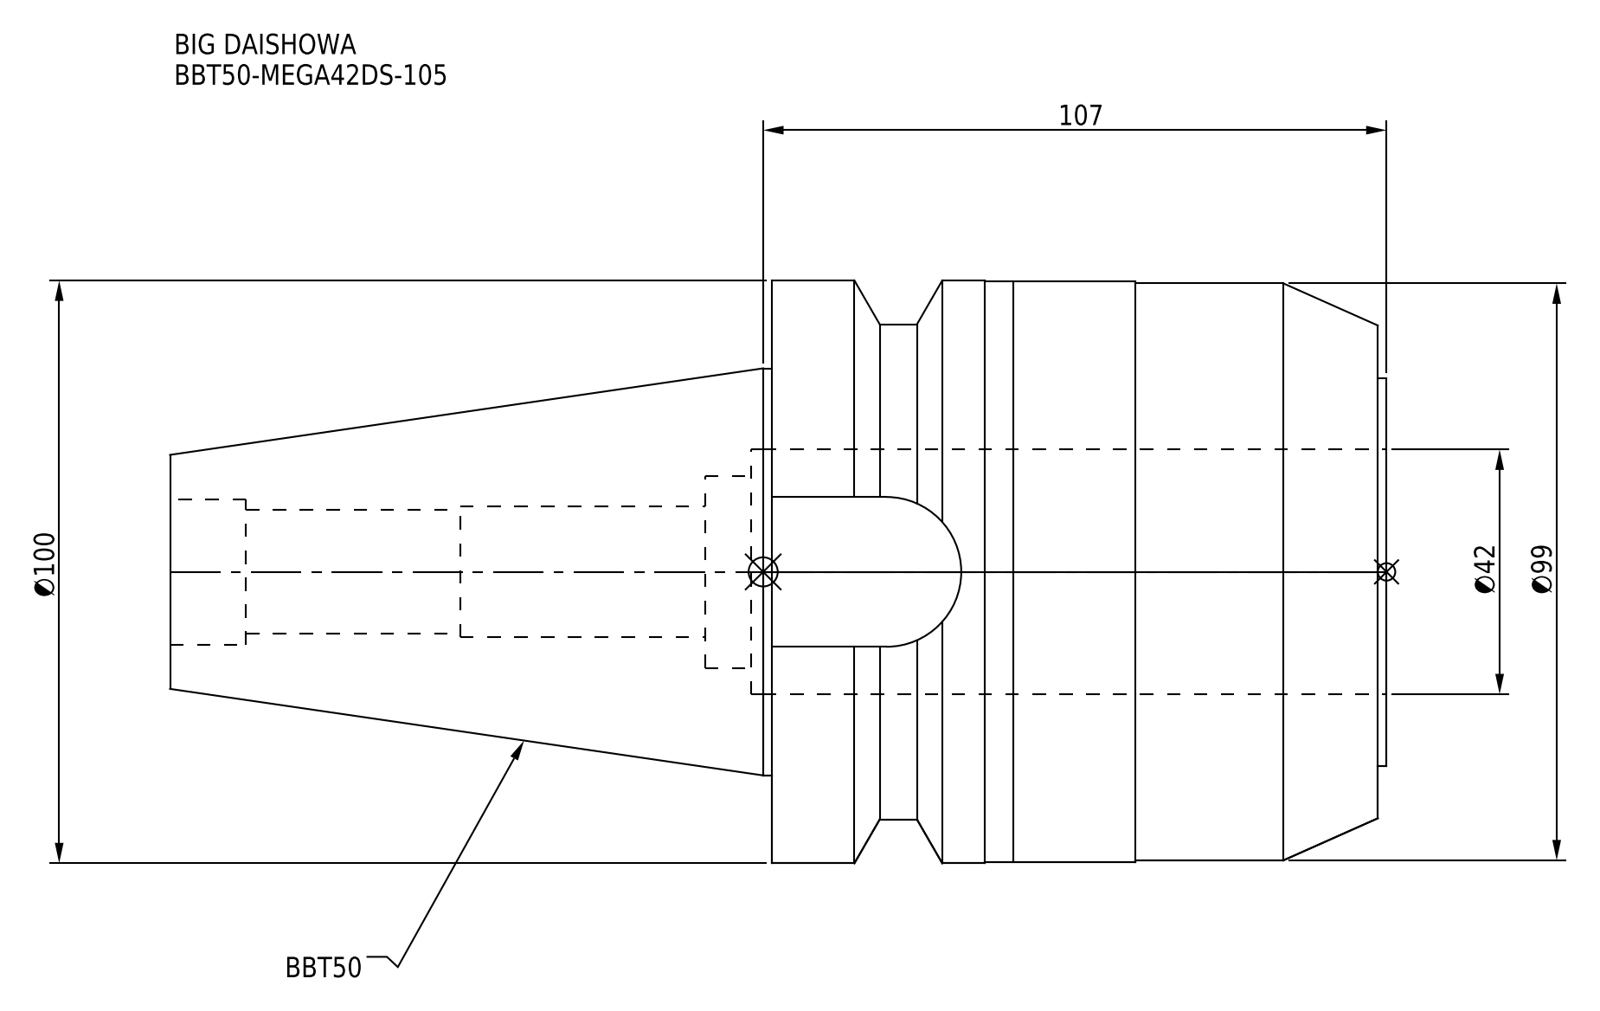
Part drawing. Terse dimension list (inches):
name: BBT50-MEGA42DS-105
written by: CREO PARAMETRIC BY PTC INC, 2016380 (AUTOMOTIVE_DESIGN)
unit: in
bodies: 1 solid, 52 faces (16 planar, 28 cylindrical, 8 other)
size: 8.22 × 3.937 × 3.937
volume: 49.76 in³; area: 132.8 in²
holes: 1× ⌀0.835, 1× ⌀0.886, 1× ⌀0.984, 1× ⌀1.299, 1× ⌀1.654
bosses: 1× ⌀3.937, 1× ⌀3.925, 1× ⌀3.898, 1× ⌀3.346, 1× ⌀2.75, 1× ⌀2.618
rounds: 1× R0.506
face distances: 4.094, 0.059, 4.154, 8.22, 8.161, 4.067, 2.787, 4.291, 4.232, 0.138
